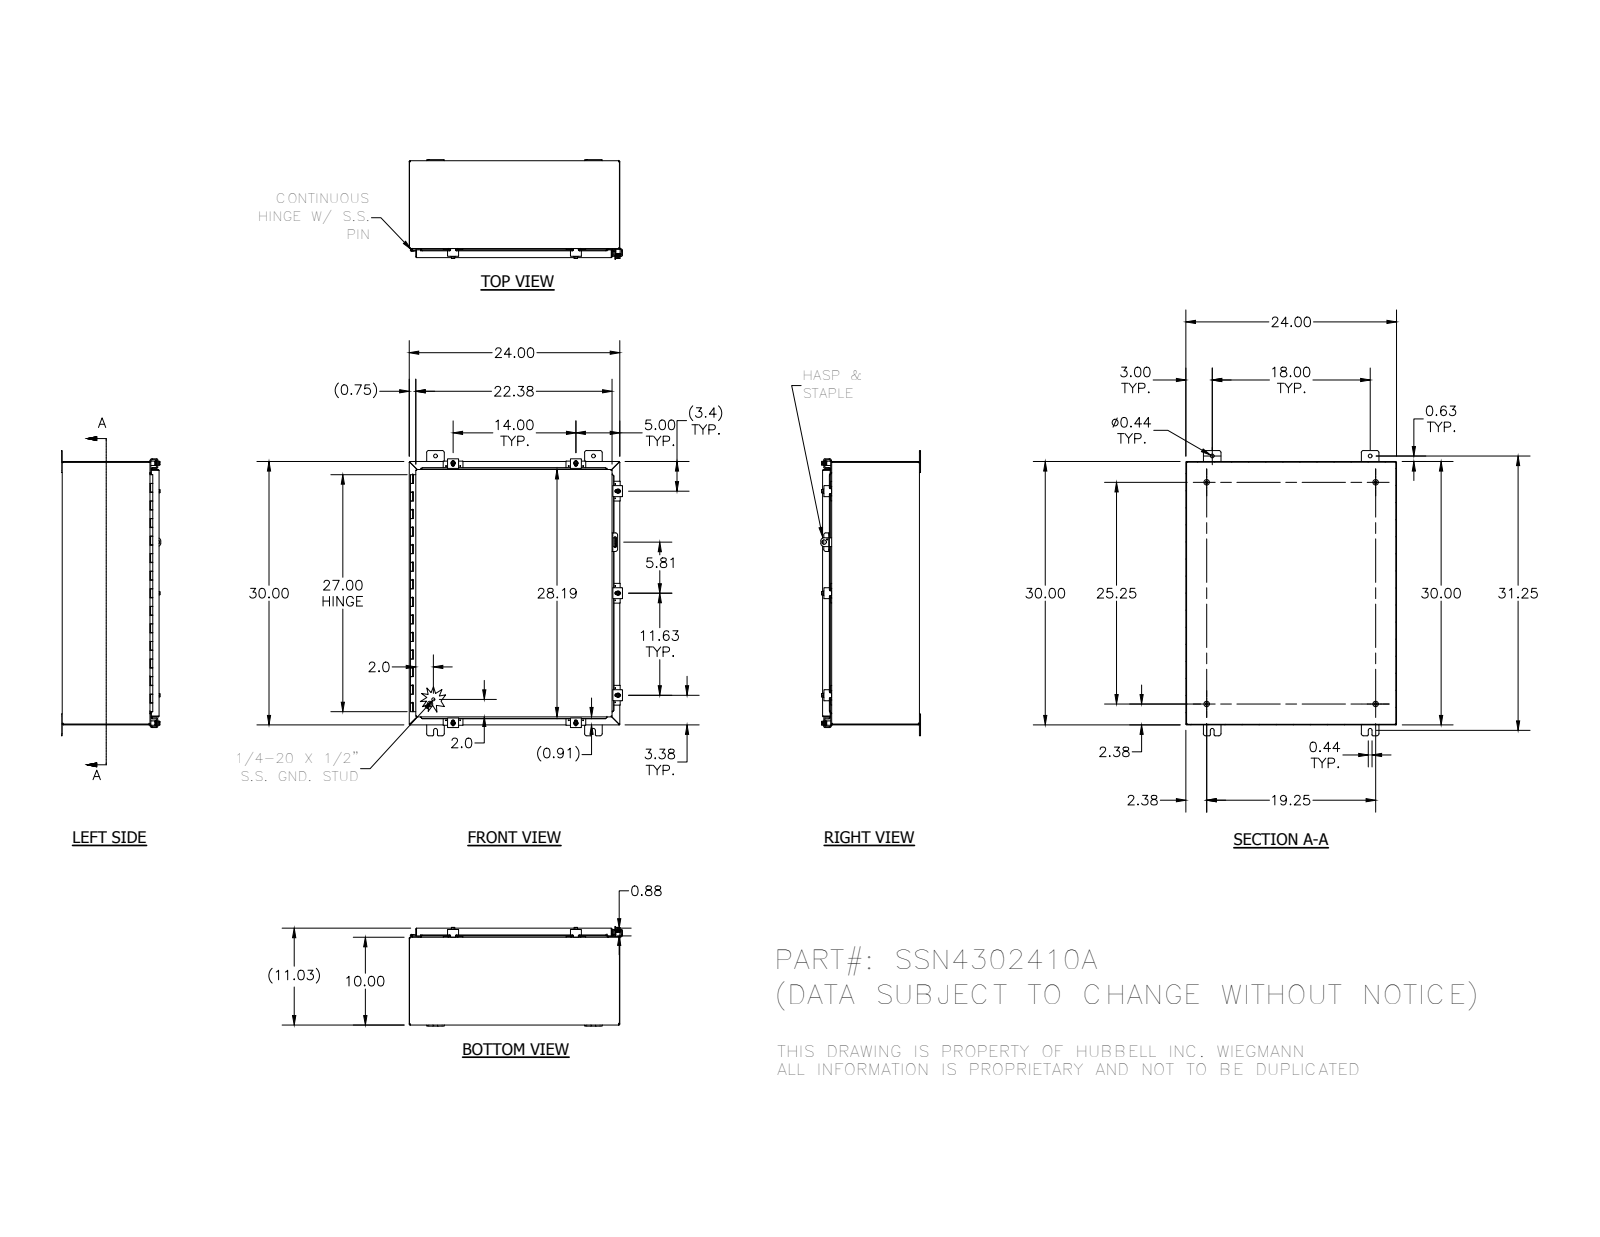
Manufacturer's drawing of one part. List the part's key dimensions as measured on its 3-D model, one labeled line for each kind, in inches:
Part name (STEP PRODUCT): 38412; 32874-30L; 30824-4; 38846 (+8 more)
STEP written by: SolidWorks 2014 (AUTOMOTIVE_DESIGN)
Units: inches
Bodies: 52 solids, 2090 faces (818 planar, 905 cylindrical, 367 other)
Overall size (bounding box): 32.5 × 24.216 × 11.355
Volume: 223.7 in³ · Surface area: 5 894 in²
Round holes (diameter × count): ⌀0.11 ×14, ⌀0.211 ×7, ⌀0.281 ×7, ⌀0.3 ×7, ⌀0.438 ×4, ⌀0.125 ×1, ⌀0.156 ×1, ⌀0.5 ×1
Round bosses / shafts (diameter × count): ⌀0.25 ×9, ⌀0.52 ×7, ⌀0.5 ×7, ⌀0.35 ×7, ⌀0.625 ×4, ⌀0.33 ×4, ⌀0.337 ×1, ⌀0.12 ×1
Partial cylindrical surfaces — rounded edges, fillets, slot ends (radius × count): R0.03 ×83, R0.125 ×37, R0.25 ×33, R0.031 ×23, R0.105 ×23, R0.062 ×18, R0.141 ×14, R0.1 ×10
Main face-to-face distances: 0.074, 10.959, 10.885, 11.033, 23.926, 29.926, 23.852, 24, 9.926, 1.033
Hole centre spacings: 0.876, 29.3, 14, 1.625, 11.625, 12.442, 13.191, 14.816
